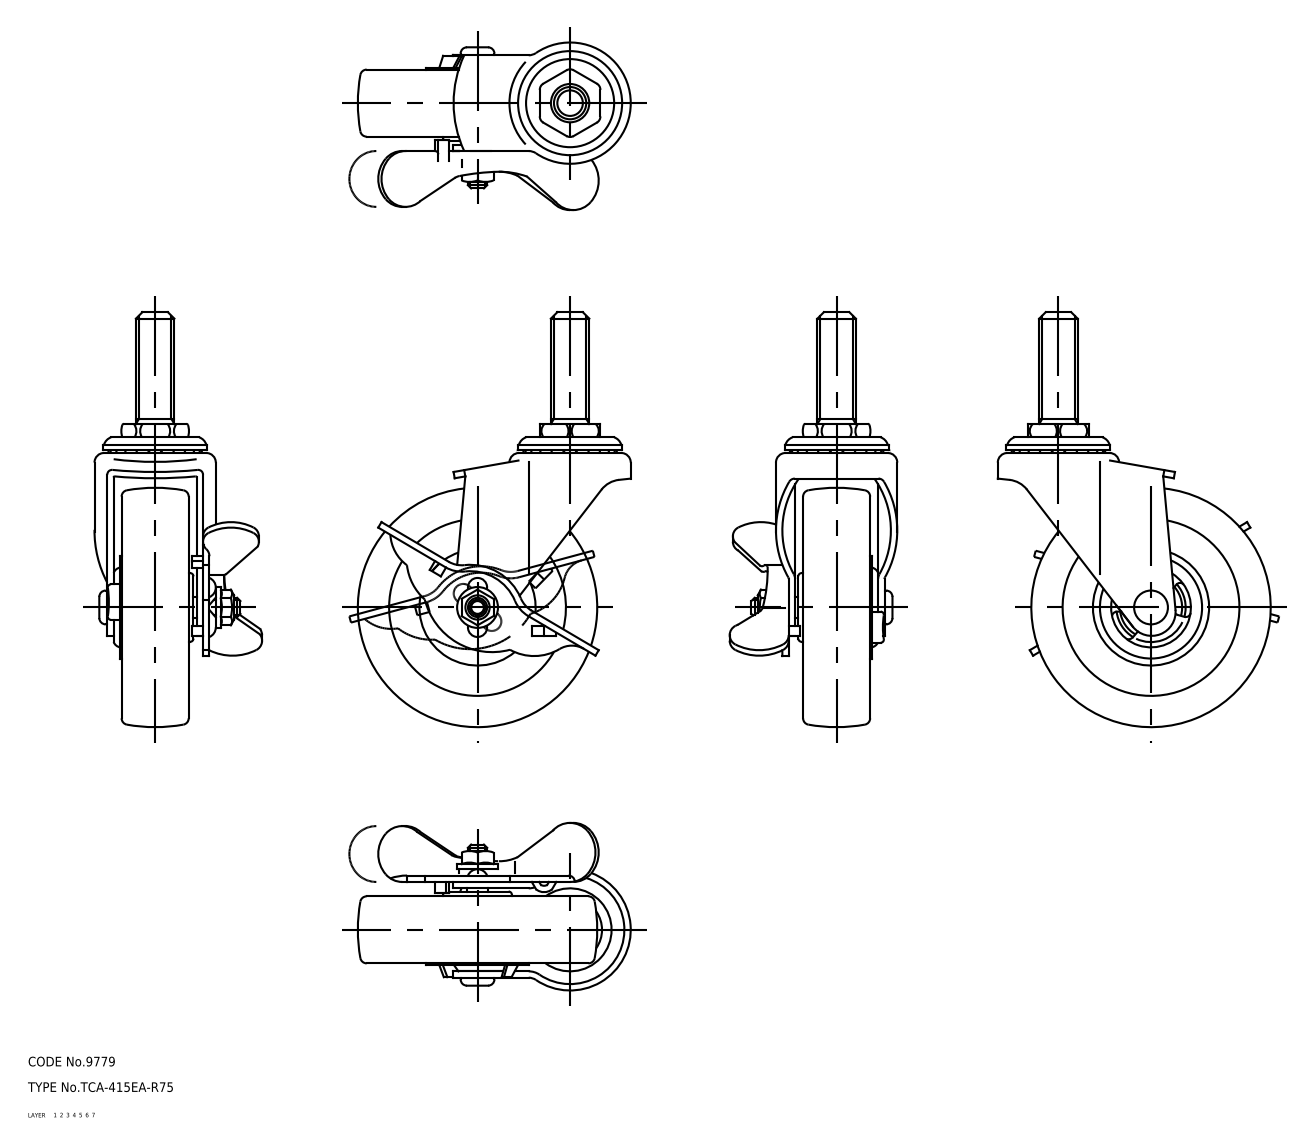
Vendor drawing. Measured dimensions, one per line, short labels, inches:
name: wheel; mounting plate; main shaft; lever (+2 more)
written by: CADfix (AUTOMOTIVE_DESIGN)
unit: in
bodies: 6 solids, 321 faces (0 planar, 0 cylindrical, 321 other)
size: 5.118 × 3.366 × 2.065
volume: 7.052 in³; area: 58.45 in²
